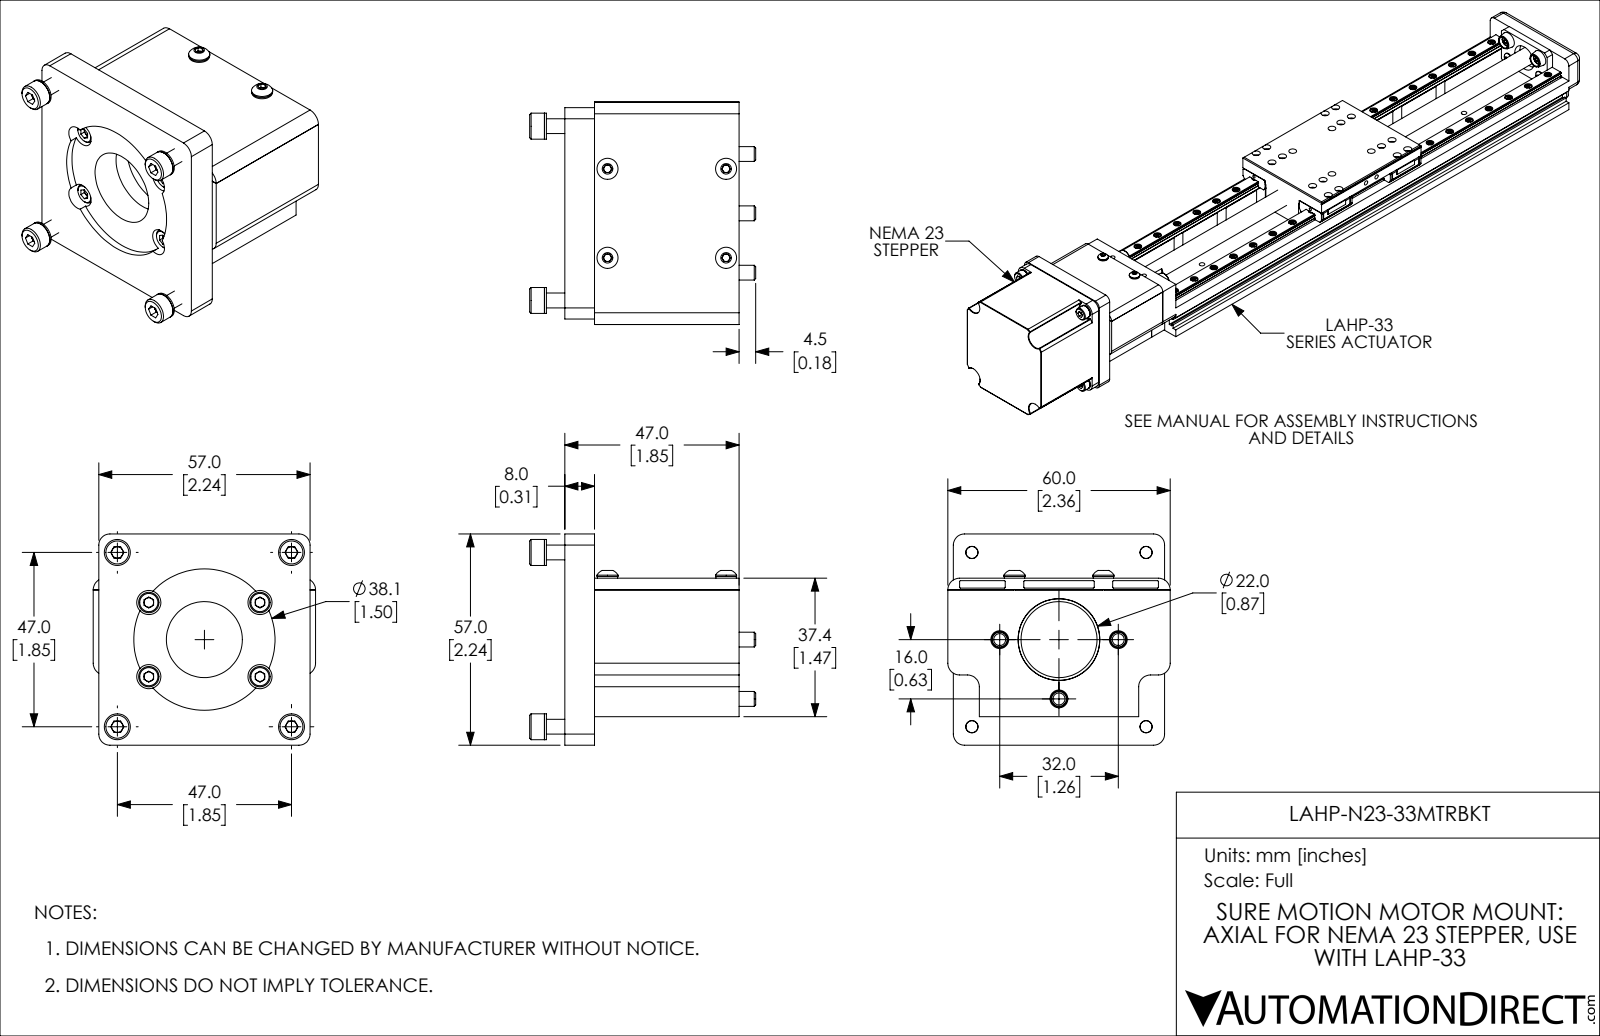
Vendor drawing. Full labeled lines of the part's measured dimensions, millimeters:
Part name (STEP PRODUCT): LAHP-N23-33MTRBKT
STEP written by: SolidWorks 2019 (CONFIG_CONTROL_DESIGN)
Units: millimetres
Bodies: 33 solids, 682 faces (315 planar, 235 cylindrical, 132 other)
Overall size (bounding box): 61 × 60 × 57
Volume: 66 270 mm³ · Surface area: 37 700 mm²
Round holes (diameter × count): ⌀2.5 ×12, ⌀3.2 ×8, ⌀3.6 ×8, ⌀4.3 ×7, ⌀3.3 ×4, ⌀6.5 ×4, ⌀4.8 ×3, ⌀8 ×3, ⌀20.5 ×1, ⌀22 ×1
Round bosses / shafts (diameter × count): ⌀5.5 ×8, ⌀3 ×8, ⌀7 ×7, ⌀4 ×7, ⌀5.7 ×4, ⌀22 ×1
Partial cylindrical surfaces — rounded edges, fillets, slot ends (radius × count): R0.3 ×12, R3.2 ×10, R3 ×4, R19.1 ×1
Main face-to-face distances: 2, 3.2, 8, 0.5, 47, 2.5, 34.2, 37.4, 34.7, 36.7
Hole centre spacings: 24.7, 45.9, 10.1, 10.3, 11.7, 16, 16.1, 18
